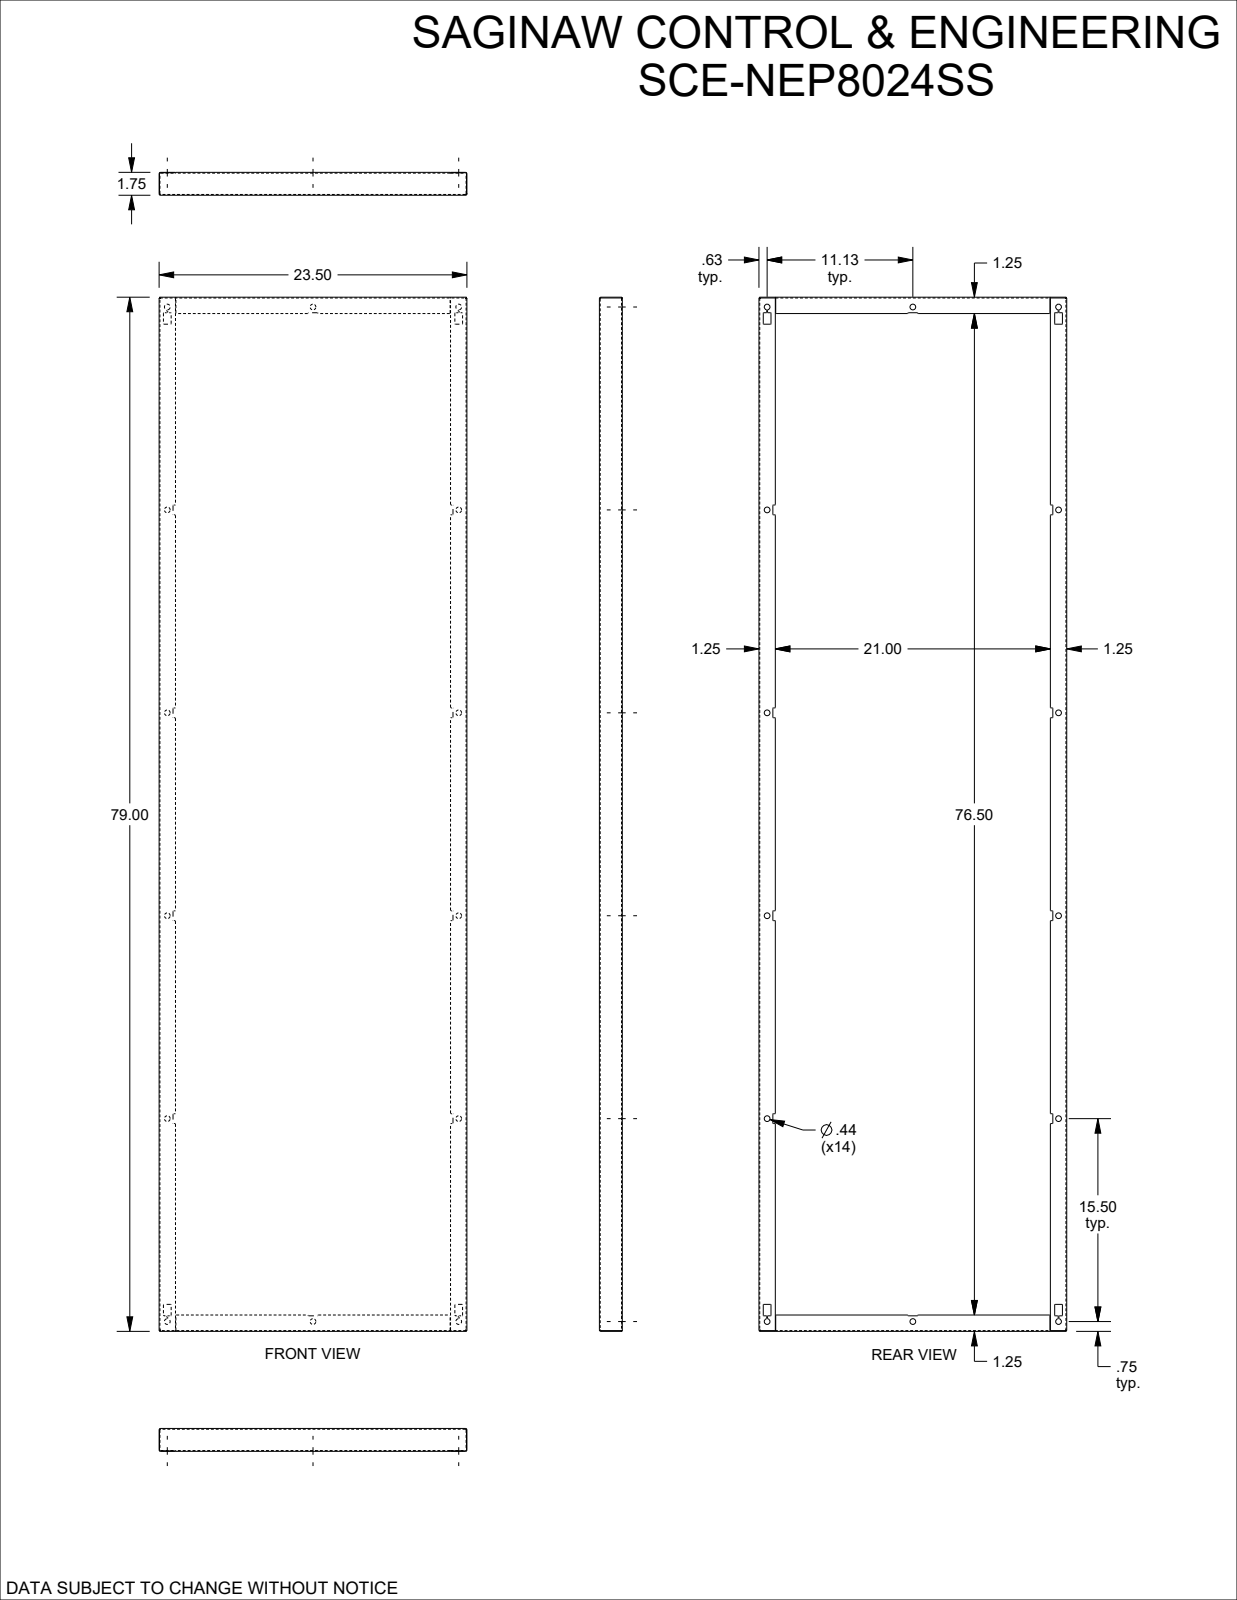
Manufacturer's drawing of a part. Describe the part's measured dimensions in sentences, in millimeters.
The part is named "SCE-NEP8024". Its 3-D file was written by "SolidWorks 2023 (AUTOMOTIVE_DESIGN)". It is 1 solid with 166 faces: 84 planar, 82 cylindrical and 0 other. Overall it measures 2006.6 by 596.9 by 44.5 millimeters. Its volume is 2 388 000 cubic millimeters and its surface area 3 151 000 square millimeters. Round holes: 14 of diameter 11.1. Partial cylindrical surfaces (rounded edges, fillets, slot ends): 68 of radius 0.8. The main face-to-face distances are 1.5, 42.9, 595.4, 44.5, 41.4, 596.9, 593.9, 2005.1, 2006.6, 2003.6. The hole center spacings are 393.7, 688.8, 787.4, 969.2, 565.2, 1181.1, 1309.3, 282.6.
